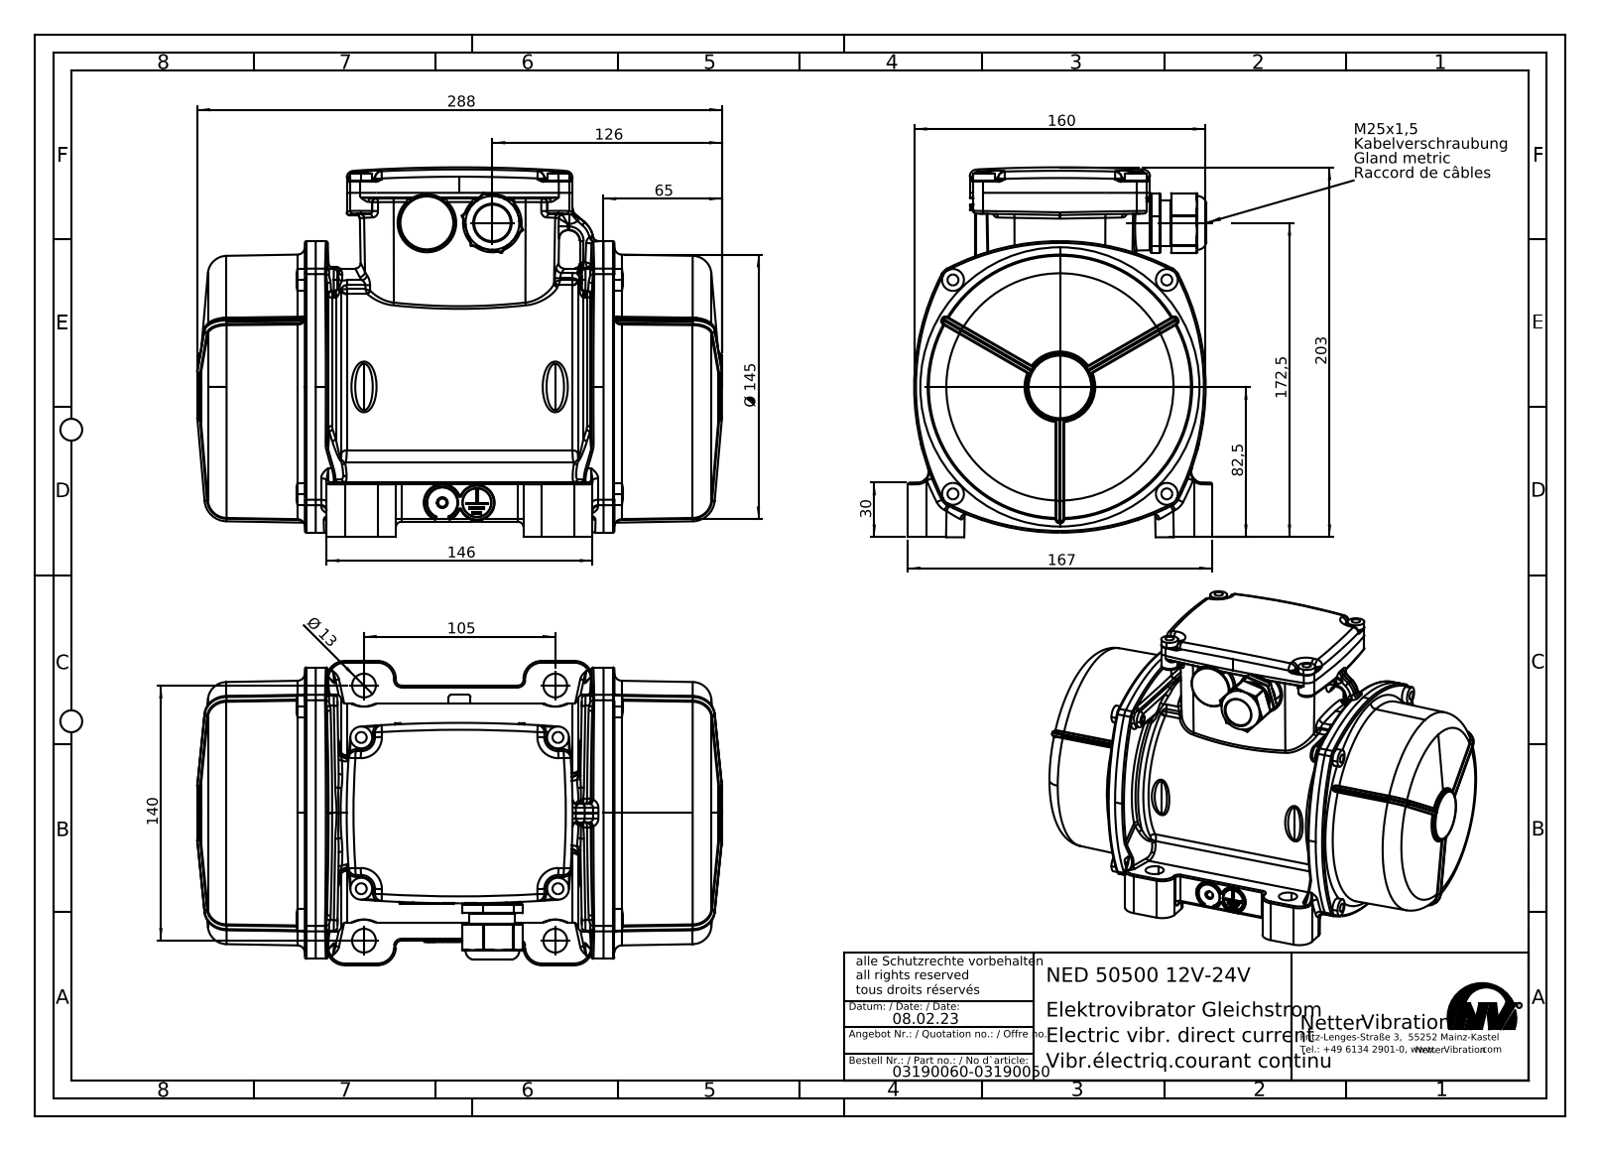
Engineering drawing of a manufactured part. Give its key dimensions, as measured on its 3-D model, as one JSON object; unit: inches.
{"part_name": "NED 50500-12V-24V #03190060-03190050", "step_written_by": "SolidWorks 2022 (AUTOMOTIVE_DESIGN)", "units": "inches", "bodies": {"solids": 2, "faces": 1796, "planar": 260, "cylindrical": 421, "other": 1115}, "overall_size": [11.339, 7.992, 6.575], "volume_in3": 295, "surface_area_in2": 395.3, "round_holes": [[0.512, 4], [0.63, 1], [0.669, 1], [0.787, 1]], "round_bosses_or_shafts": [[0.472, 8], [4.724, 1], [0.984, 1], [0.748, 1]], "partial_cylinders_radius": [[0.02, 50], [0.059, 34], [0.118, 34], [0.079, 30], [0.394, 20], [0.039, 13], [0.157, 12], [0.485, 6]], "face_to_face_distances": [6.693, 6.043, 0.531, 2.323, 9.016, 4.724, 3.799, 0.537, 0.925, 0.985], "hole_center_spacings": [4.134, 5.512, 6.89, 0.748, 6.053, 6.139]}
